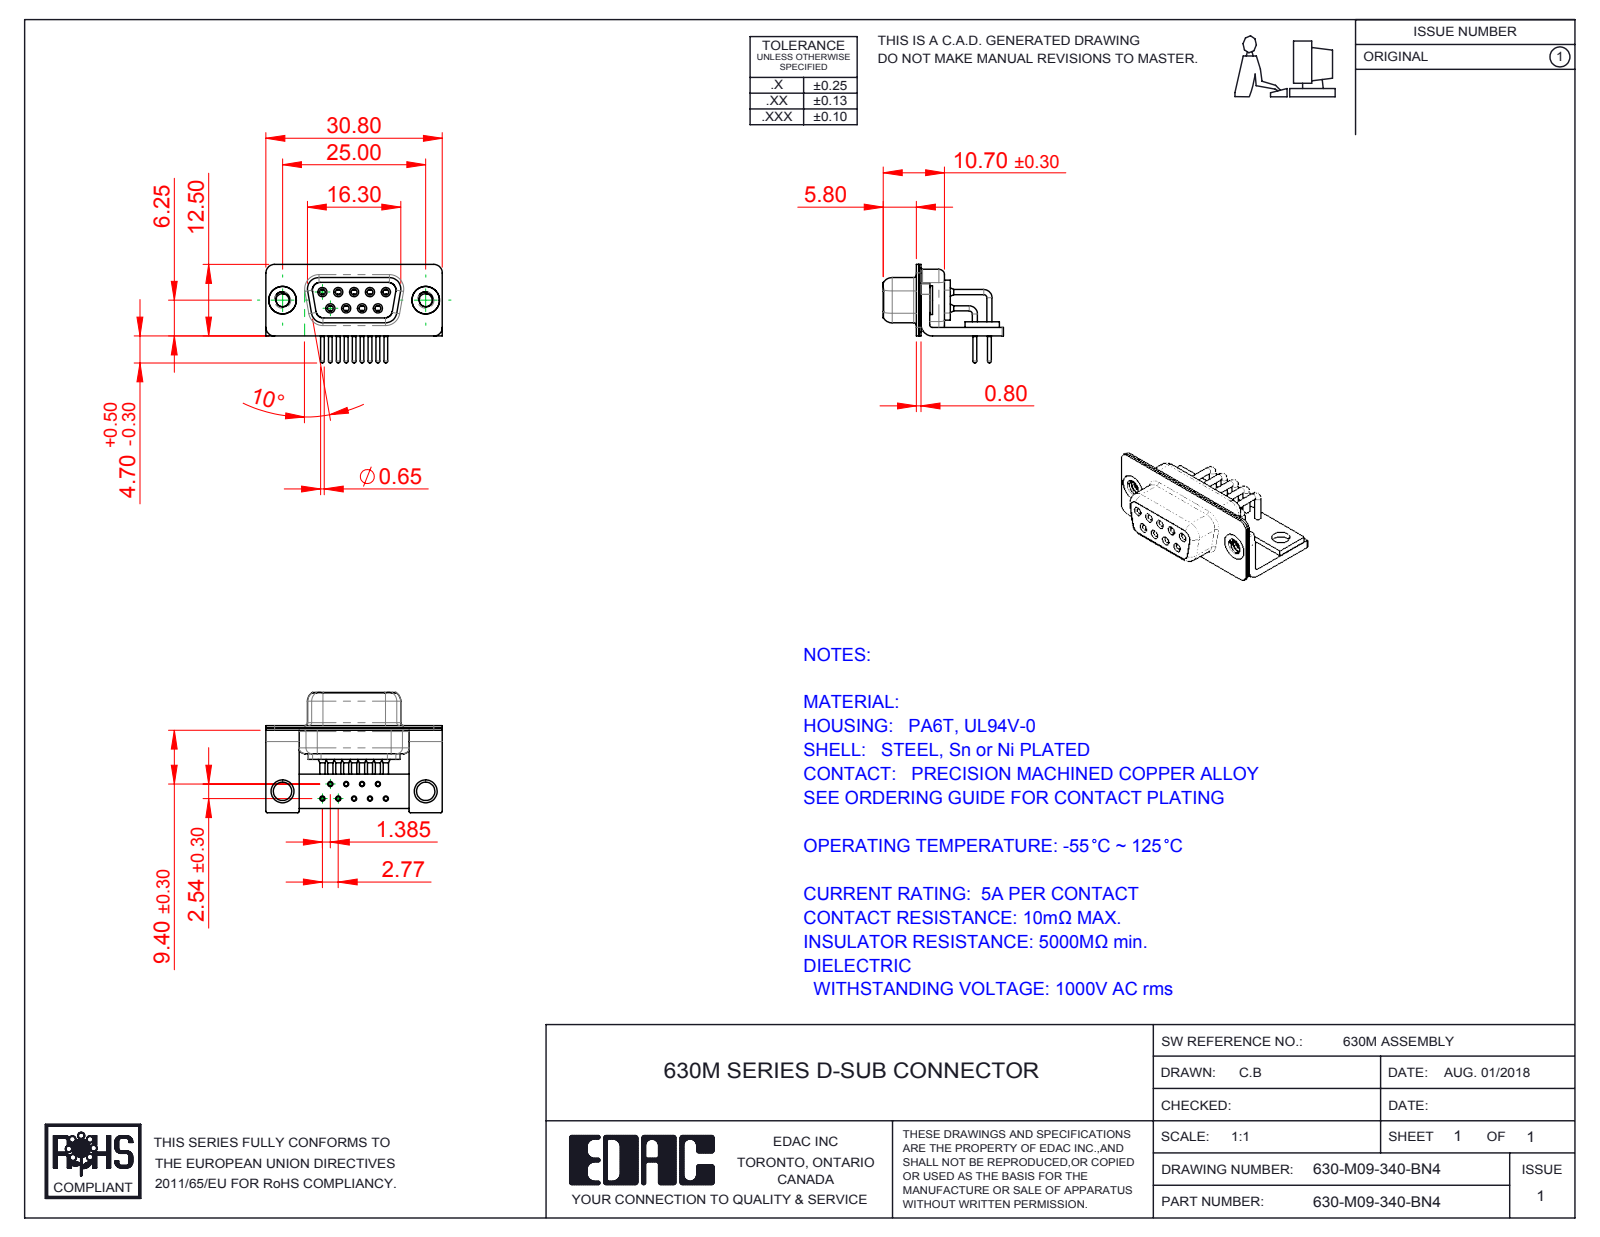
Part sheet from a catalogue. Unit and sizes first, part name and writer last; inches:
Units: inches
Overall size (bounding box): 1.213 × 0.827 × 0.677
Round holes (diameter × count): ⌀0.035 ×9, ⌀0.039 ×9, ⌀0.043 ×9, ⌀0.067 ×9, ⌀0.071 ×9, ⌀0.079 ×9, ⌀0.089 ×2, ⌀0.126 ×2, ⌀0.157 ×2, ⌀0.189 ×2
Round bosses / shafts (diameter × count): ⌀0.063 ×9, ⌀0.059 ×9, ⌀0.035 ×9, ⌀0.026 ×9, ⌀0.197 ×2, ⌀0.193 ×2
Partial cylindrical surfaces — rounded edges, fillets, slot ends (radius × count): R0.01 ×16, R0.059 ×16, R0.079 ×13, R0.053 ×8, R0.063 ×8, R0.02 ×5, R0.024 ×4, R0.026 ×4
Main face-to-face distances: 0.016, 0.031, 0.059, 0.091, 0.075, 0.039, 0.368, 0.057, 0.098, 0.352
Hole centre spacings: 0.109, 0.218, 0.124, 0.192, 0.327, 0.114, 0.114, 0.198
Volume: 0.134 in³ · Surface area: 8.795 in²
Bodies: 17 solids, 824 faces (228 planar, 384 cylindrical, 212 other)
Part name (STEP PRODUCT): 630M Contact Row 2; 630M Shell Front_09 Contacts; 630M 4-40 Threaded Rivet_Stabilizer; 630M Shell Rear_09 Contacts (+5 more)
STEP written by: SolidWorks 2016 (CONFIG_CONTROL_DESIGN)
